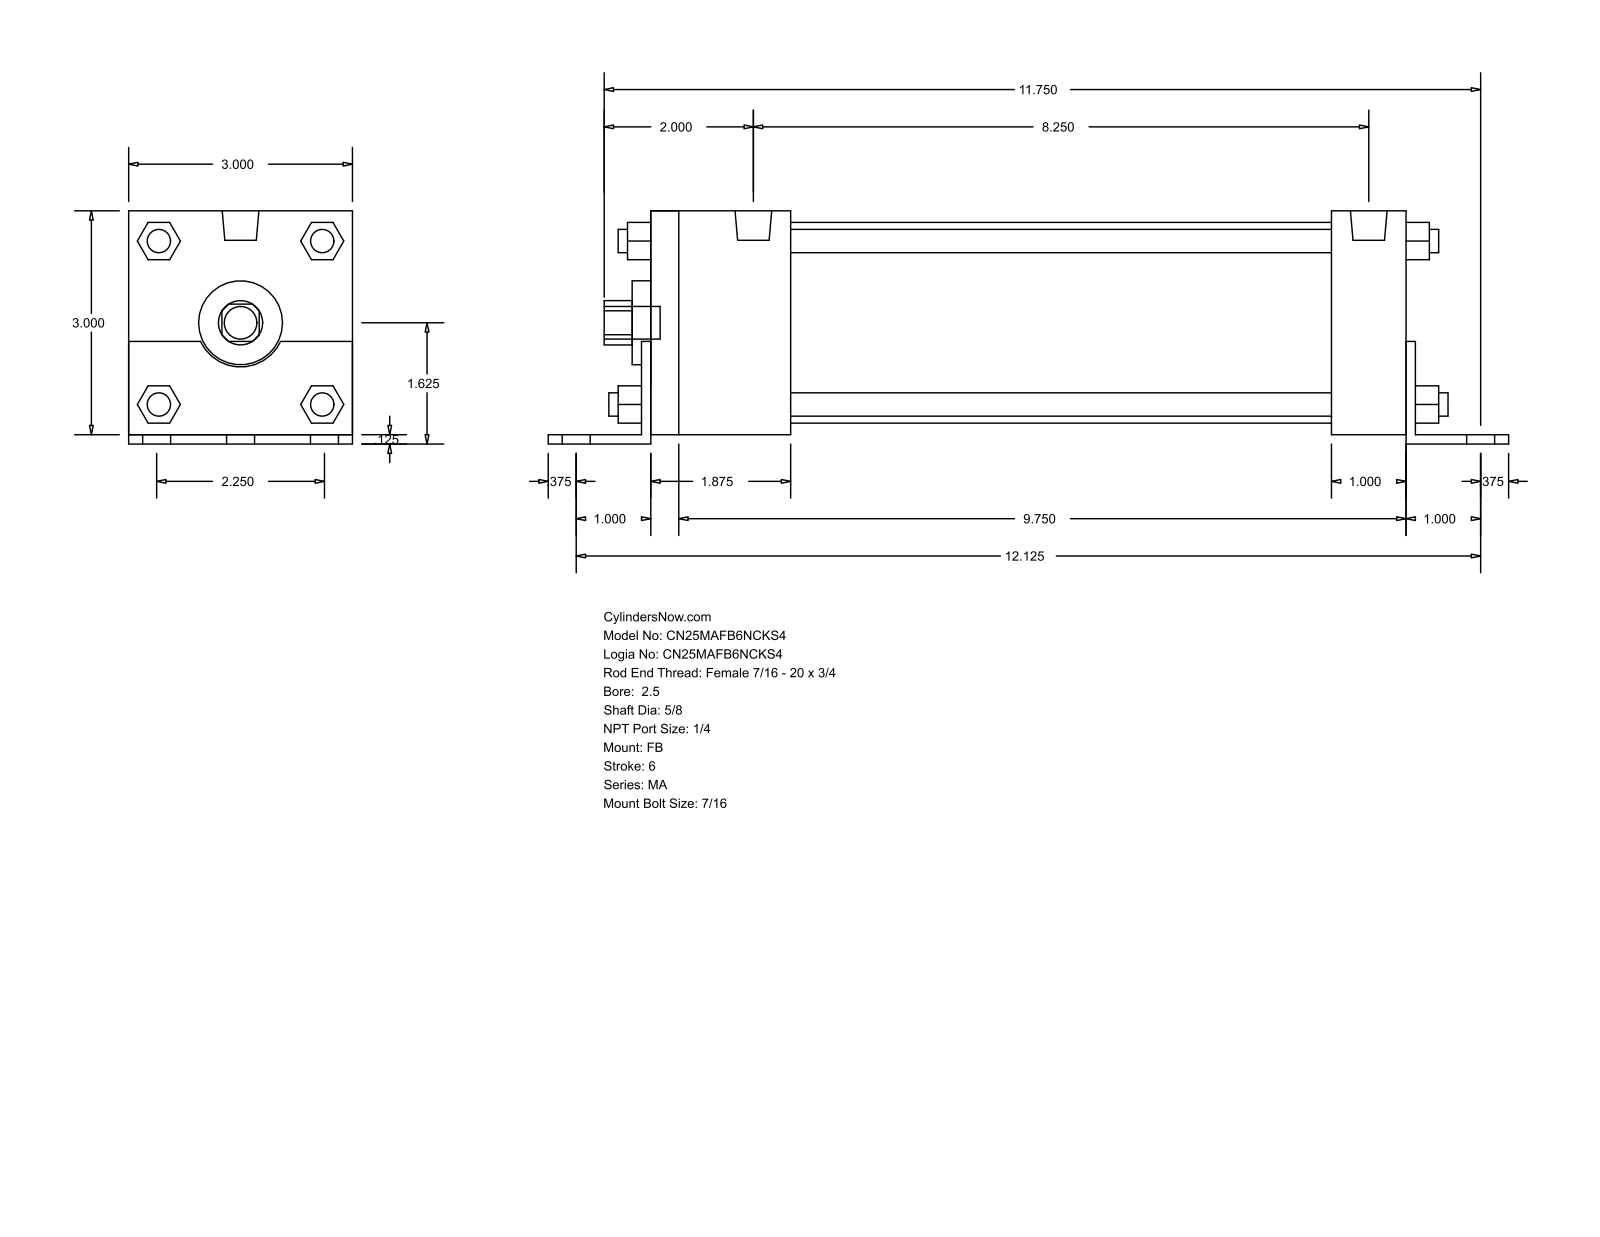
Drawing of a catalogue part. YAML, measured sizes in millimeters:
part_name: "MA_FB__0250_0.625"
step_written_by: "GSSL Pune (CONFIG_CONTROL_DESIGN)"
units: millimeters
bodies: {solids: 0, faces: 140, planar: 105, cylindrical: 35, other: 0}
overall_size: [327.02, 79.38, 76.2]
round_holes:
  - {diameter: 15.88, count: 1}
  - {diameter: 28.57, count: 1}
  - {diameter: 68.33, count: 1}
round_bosses_or_shafts:
  - {diameter: 7.94, count: 8}
  - {diameter: 11.11, count: 7}
  - {diameter: 12.49, count: 2}
partial_cylinders:
  - {radius: 7.54, count: 1}
  - {radius: 15.05, count: 1}
face_to_face_distances: [76.2, 3.17, 79.37, 3.18, 260.35, 257.17, 28.58, 47.62, 25.4, 263.53]
